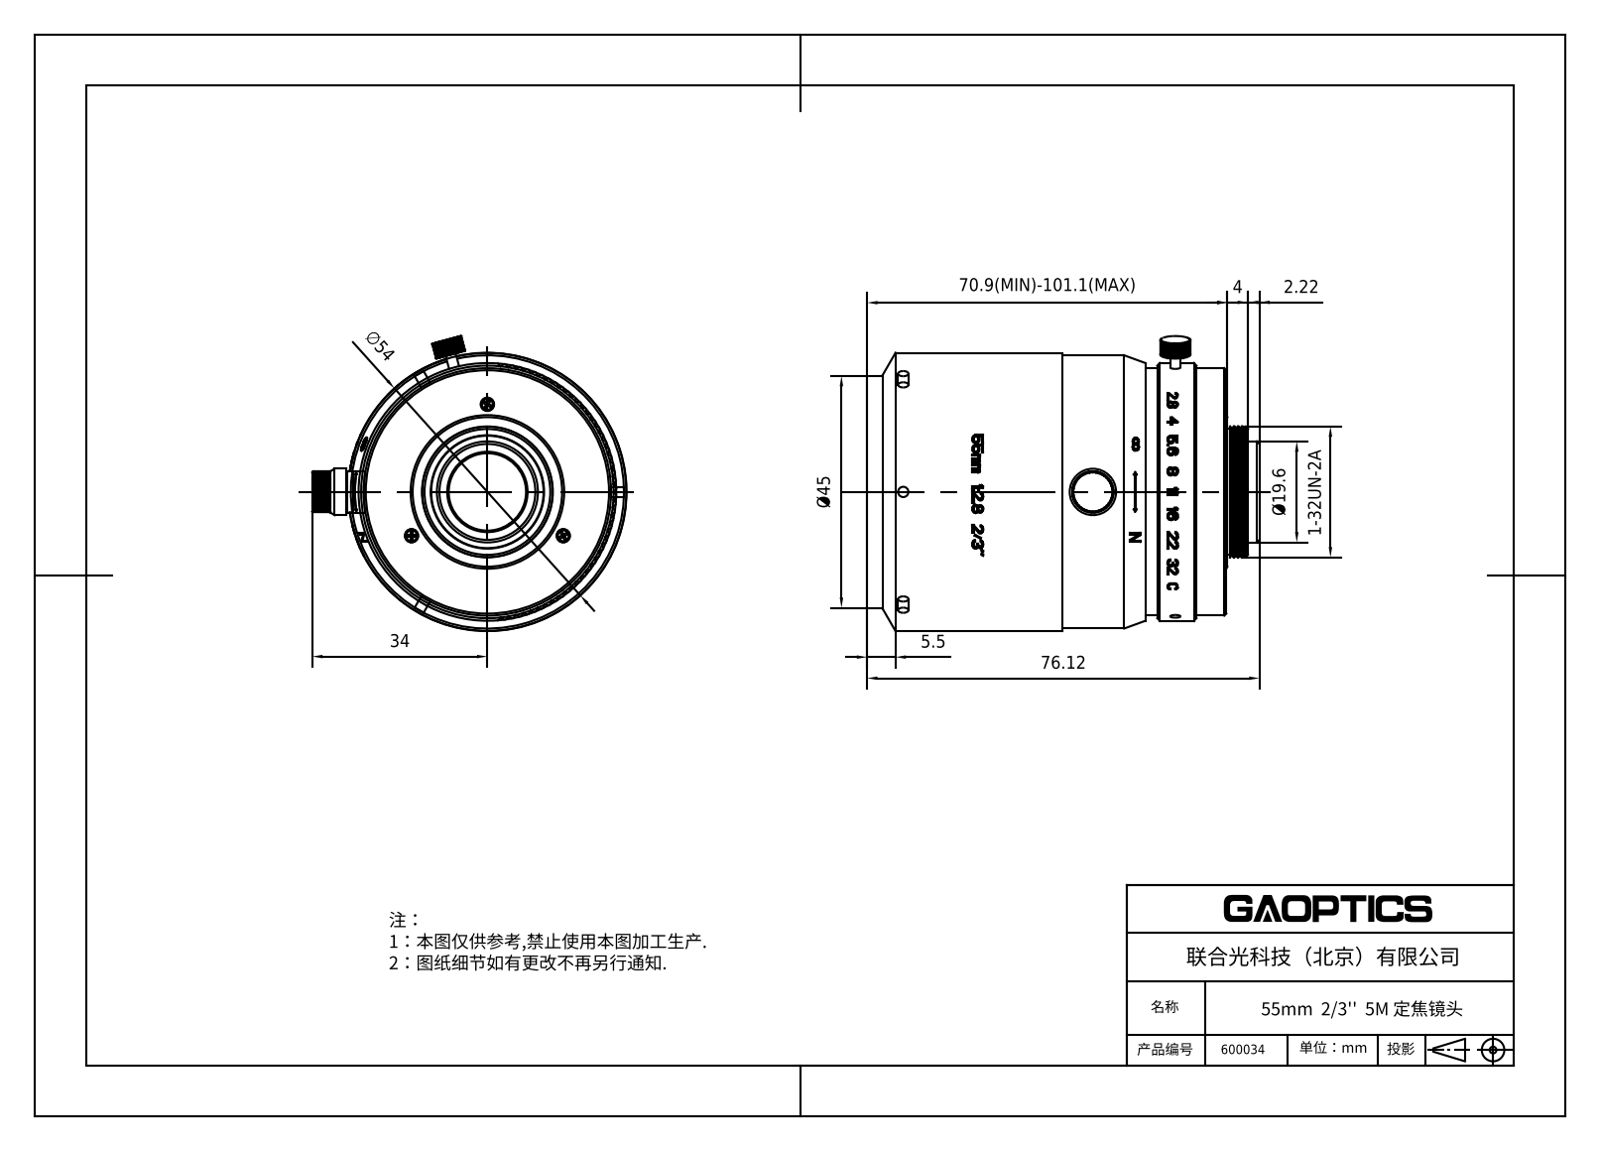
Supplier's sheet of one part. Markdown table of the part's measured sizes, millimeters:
| quantity | value |
| --- | --- |
| part name | 600034 |
| STEP written by | SolidWorks 2020 (CONFIG_CONTROL_DESIGN) |
| units | millimeters |
| bodies | 0 solids, 2078 faces (932 planar, 292 cylindrical, 854 other) |
| overall size | 76.12 × 61 × 57.24 |
| round holes (diameter × count) | 1.6 × 3, 1.8 × 3, 2.6 × 3, 2 × 2, 3.6 × 1, 6 × 1, 6.98 × 1, 7 × 1, 7.25 × 1, 8 × 1, 9 × 1, 15 × 1 |
| round bosses / shafts (diameter × count) | 2.5 × 3, 2 × 3, 1.7 × 3, 53.9 × 1, 53 × 1, 45.4 × 1, 45 × 1, 43 × 1 |
| partial cylindrical surfaces (radius × count) | 4 × 1, 24.95 × 1, 25 × 1, 27 × 1 |
| main face-to-face distances | 7.38, 1.8, 5.58, 1, 2.8, 4.58, 52.4, 56.98, 57.98, 59.78 |
| hole center spacings | 17, 29.44, 36.8 |
